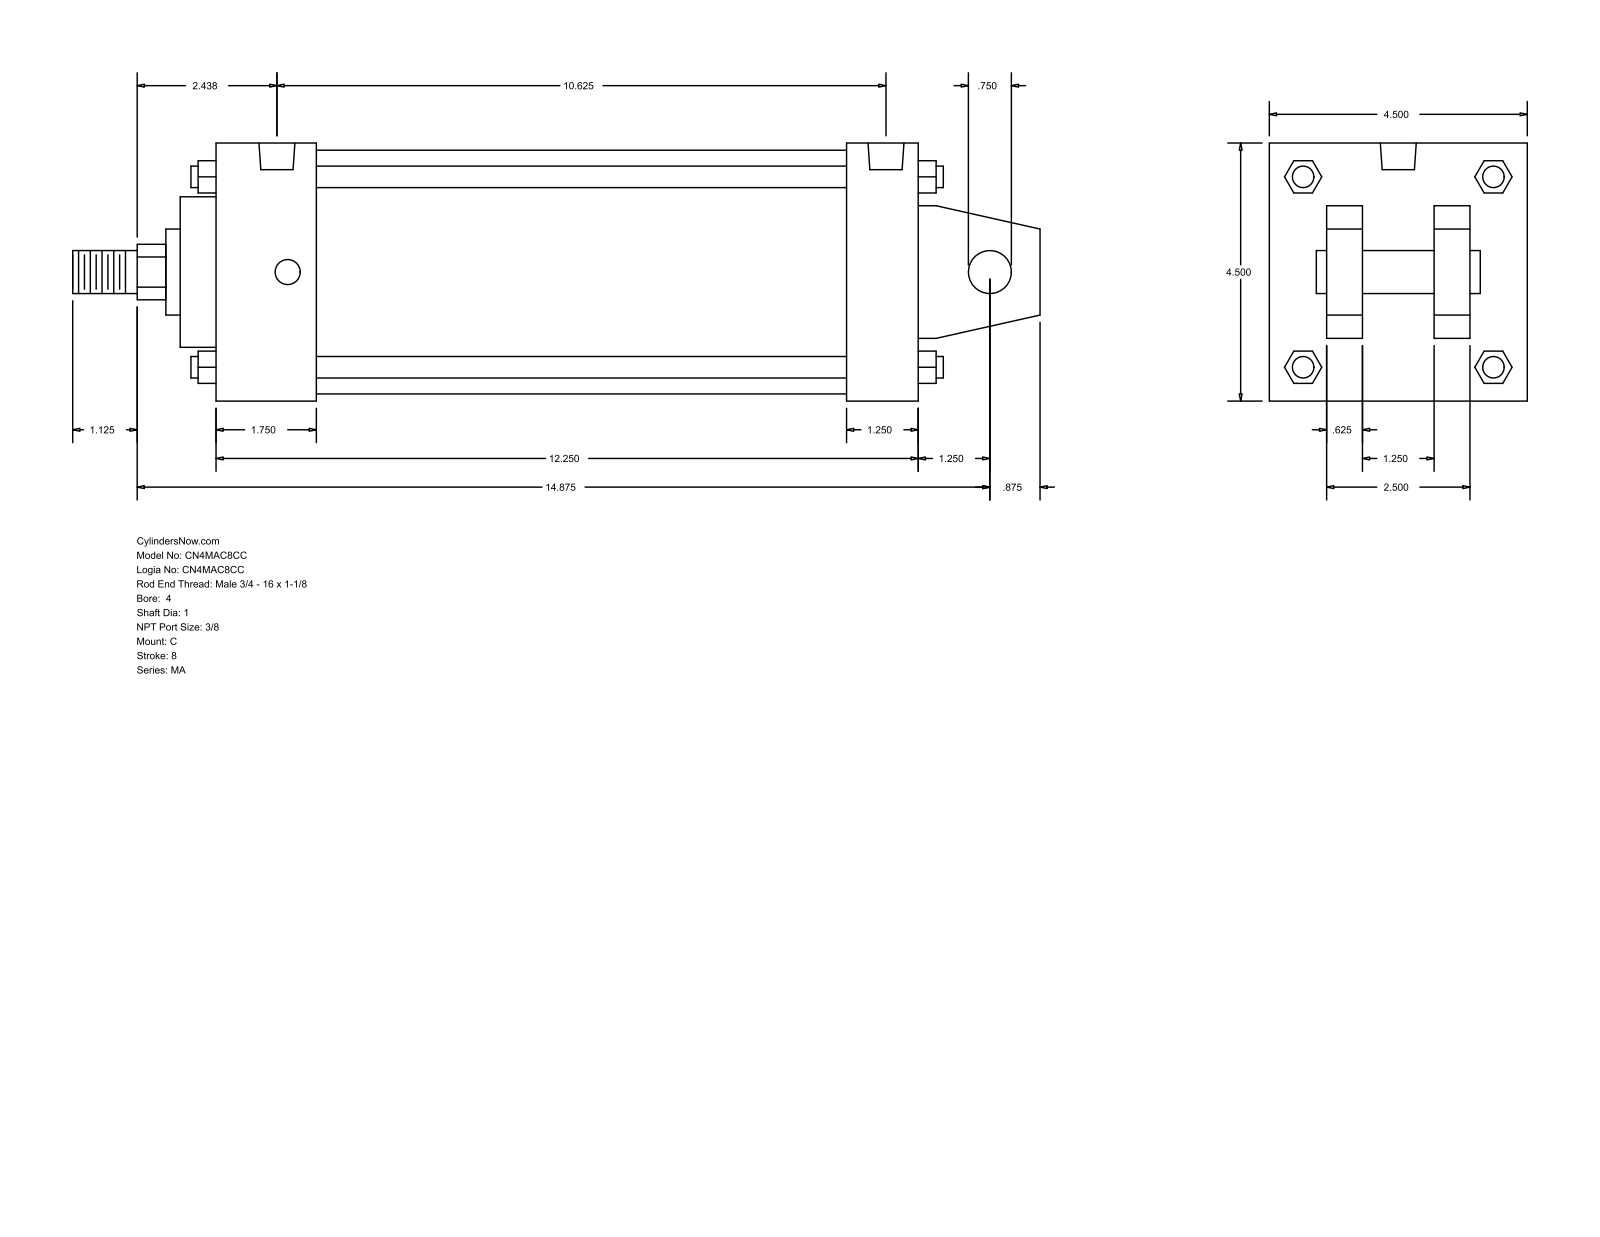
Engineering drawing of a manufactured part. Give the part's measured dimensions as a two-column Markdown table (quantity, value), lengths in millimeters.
| quantity | value |
| --- | --- |
| part name | MA_C__0400_1 |
| STEP written by | GSSL Pune (CONFIG_CONTROL_DESIGN) |
| units | millimeters |
| bodies | 0 solids, 141 faces (109 planar, 32 cylindrical, 0 other) |
| overall size | 428.62 × 114.3 × 114.3 |
| round holes (diameter × count) | 11.11 × 4, 15.93 × 2 |
| round bosses / shafts (diameter × count) | 9.53 × 4, 19.05 × 2, 107.95 × 1, 66.67 × 1, 38.1 × 1, 25.4 × 1 |
| partial cylindrical surfaces (radius × count) | 12.29 × 1 |
| main face-to-face distances | 114.3, 311.15, 15.87, 73.03, 41.27, 25.4, 88.9, 47.63, 279.4, 31.75 |
| hole center spacings | 260.35, 4.76, 4.77, 265.11, 265.12, 269.88 |
